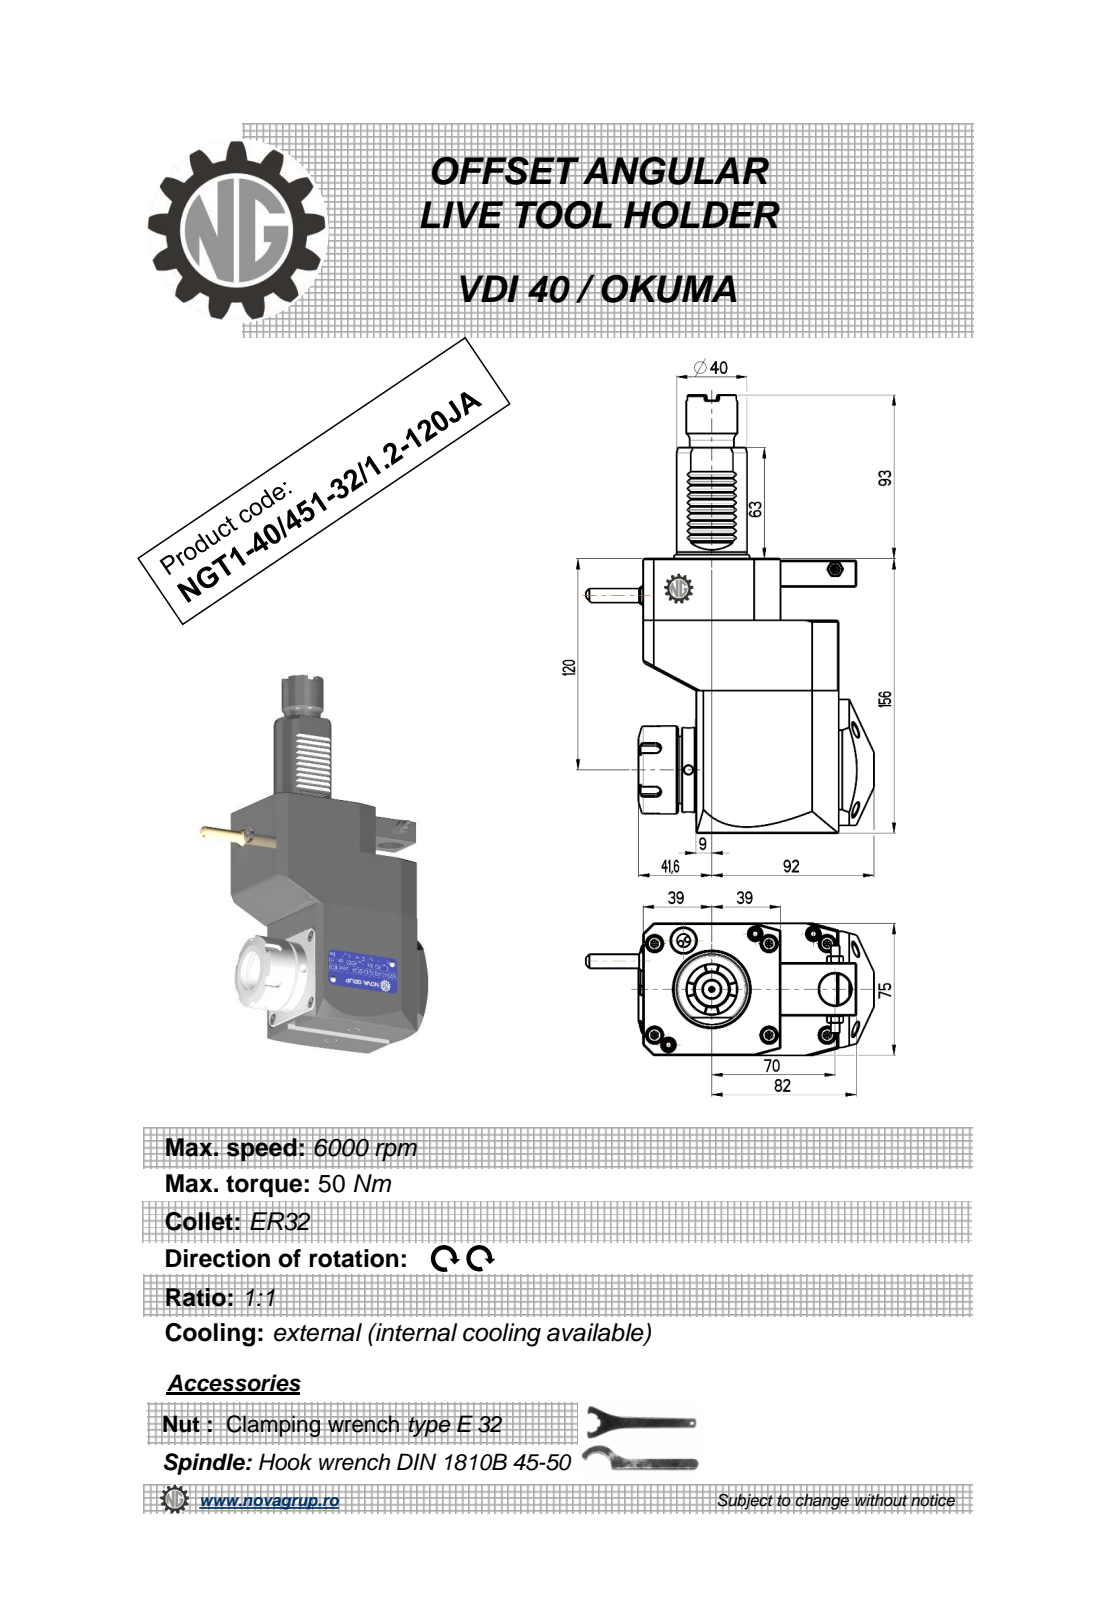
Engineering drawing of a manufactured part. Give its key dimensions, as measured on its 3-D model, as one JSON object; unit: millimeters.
{"part_name": "NGT1_40_451_32_1_2_120JA", "step_written_by": "PRO/ENGINEER BY PARAMETRIC TECHNOLOGY CORPORATION, 2010280 (CONFIG_CONTROL_DESIGN)", "units": "millimeters", "bodies": {"solids": 1, "faces": 479, "planar": 217, "cylindrical": 97, "other": 165}, "overall_size": [249, 163.5, 76.6], "volume_mm3": 1213000, "surface_area_mm2": 92072, "round_holes": [[5, 3], [3, 1], [4.2, 1], [9.5, 1], [18, 1], [26.8, 1], [27, 1]], "round_bosses_or_shafts": [[50, 1], [48, 1], [41, 1], [40, 1], [29, 1], [26.58, 1], [25, 1], [10, 1]], "partial_cylinders_radius": [[0.26, 12], [0.3, 10], [0.2, 6], [3, 5], [0.5, 1], [10, 1], [40, 1]], "face_to_face_distances": [75, 156, 111, 30, 121, 35, 81, 48, 33, 78], "hole_center_spacings": [13.25, 20.93, 70, 83.25, 100.28, 112.5, 141.16]}
